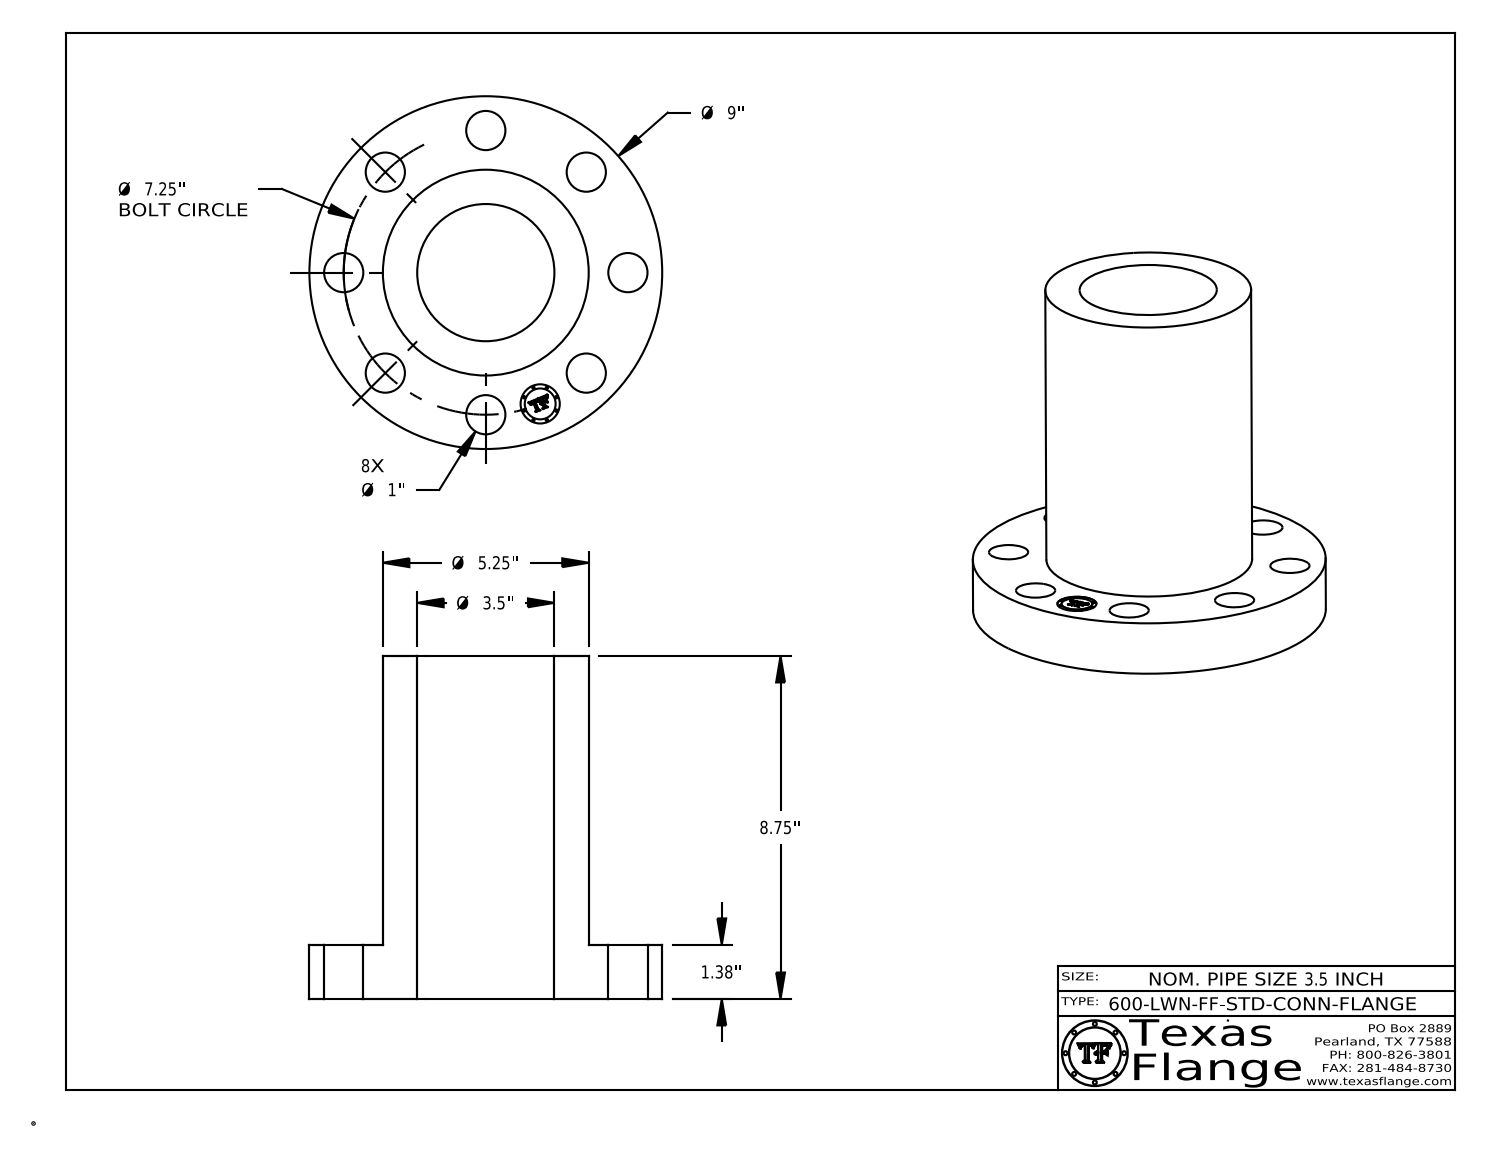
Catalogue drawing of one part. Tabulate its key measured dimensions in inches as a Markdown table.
| quantity | value |
| --- | --- |
| part name | 3.5-600-LWN-FF-STD-CONN-FLANGE |
| STEP written by | CATIA V5 STEP AP214 (AUTOMOTIVE_DESIGN) |
| units | inches |
| bodies | 1 solid, 410 faces (368 planar, 42 cylindrical, 0 other) |
| overall size | 9 × 9 × 8.75 |
| volume | 154.5 in³ |
| surface area | 387 in² |
| round holes (diameter × count) | 1 × 9, 3.5 × 1 |
| round bosses / shafts (diameter × count) | 0.061 × 8, 9 × 1, 5.25 × 1, 0.788 × 1 |
| main face-to-face distances | 1.38, 8.75, 7.37, 1.375, 7.375, 0.298, 0.292, 0.054, 0.193, 0.248 |
| hole center spacings | 3.625, 2.774, 5.127, 6.698, 7.25, 1.415, 7.111, 4.028 |
